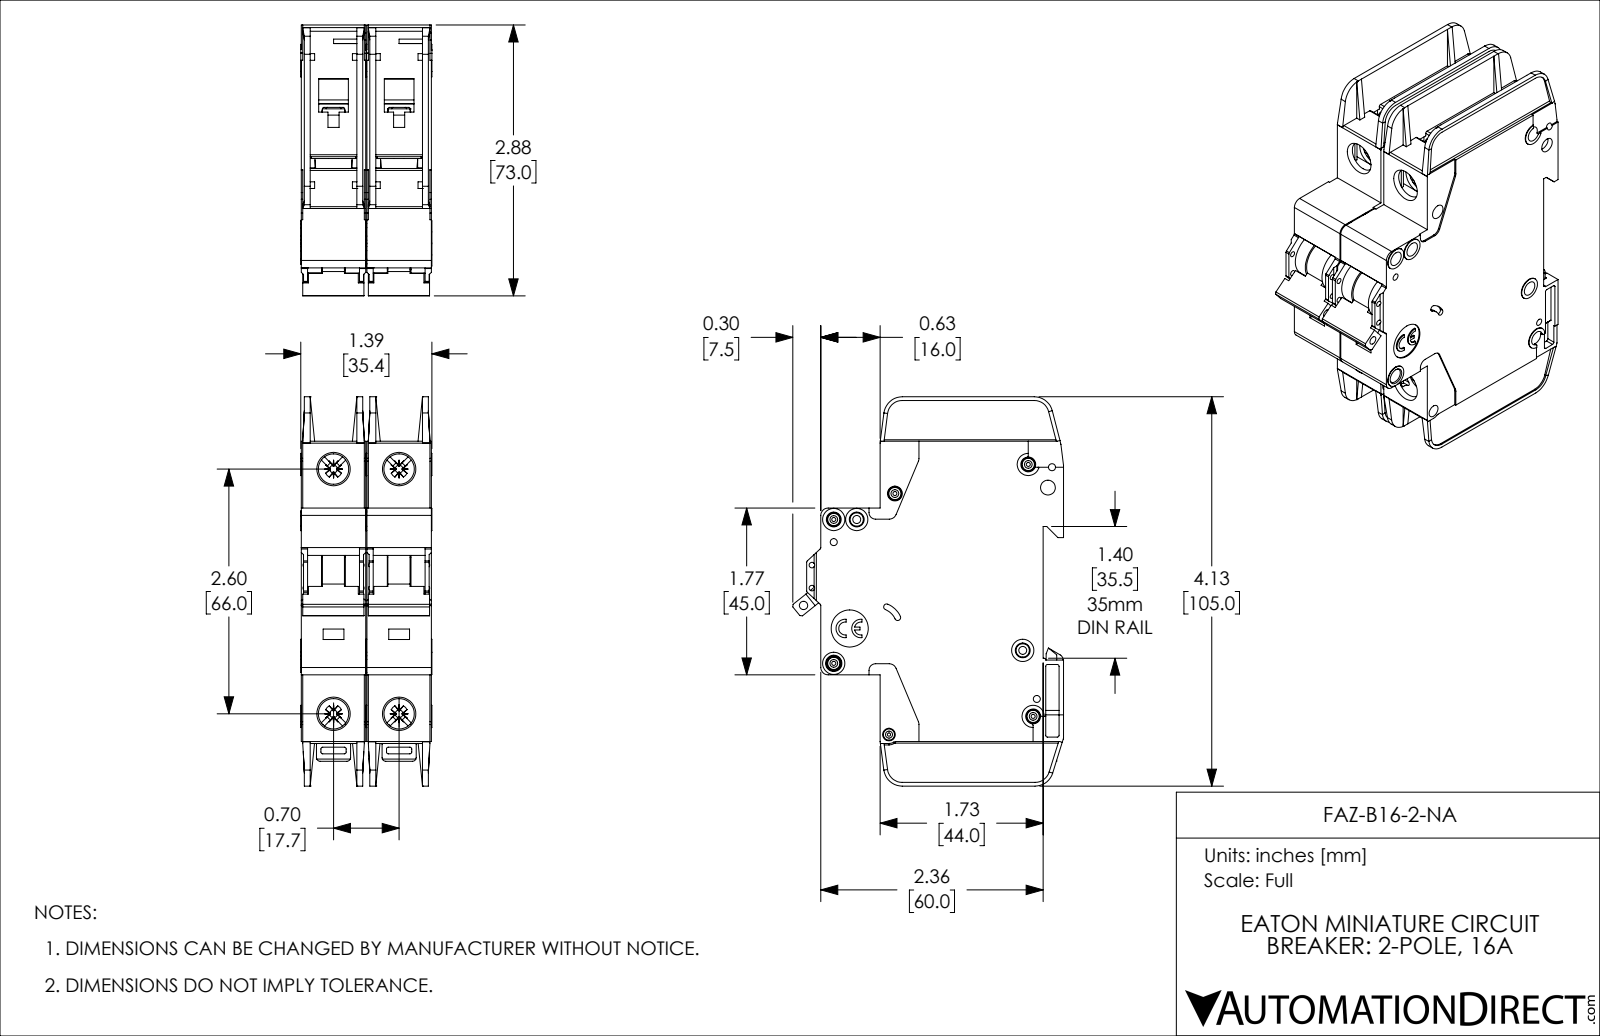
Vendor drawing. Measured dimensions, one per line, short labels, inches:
name: FAZ-B16-2-NA
written by: SolidWorks 2019 (AUTOMOTIVE_DESIGN)
unit: in
bodies: 2 solids, 2254 faces (1342 planar, 714 cylindrical, 198 other)
size: 4.134 × 2.876 × 1.394
volume: 9.365 in³; area: 82.01 in²
holes: 8× ⌀0.157, 5× ⌀0.043, 4× ⌀0.075, 4× ⌀0.323, 2× ⌀0.059, 2× ⌀0.085, 1× ⌀0.035, 1× ⌀0.089, 1× ⌀0.098, 1× ⌀0.134, 1× ⌀0.394
bosses: 5× ⌀0.13, 4× ⌀0.236, 3× ⌀0.118, 2× ⌀0.098
rounds: 57× R0.02, 20× R0.016, 14× R0.039, 10× R0.079, 8× R0.043, 5× R0.008, 5× R0.197, 4× R0.01
face distances: 0.697, 0.047, 0.685, 0.591, 0.094, 0.638, 0.543, 1.382, 0.744, 0.65
hole spacings: 0.244, 0.537, 0.697, 0.87, 2.598, 2.69, 0.189, 0.199
